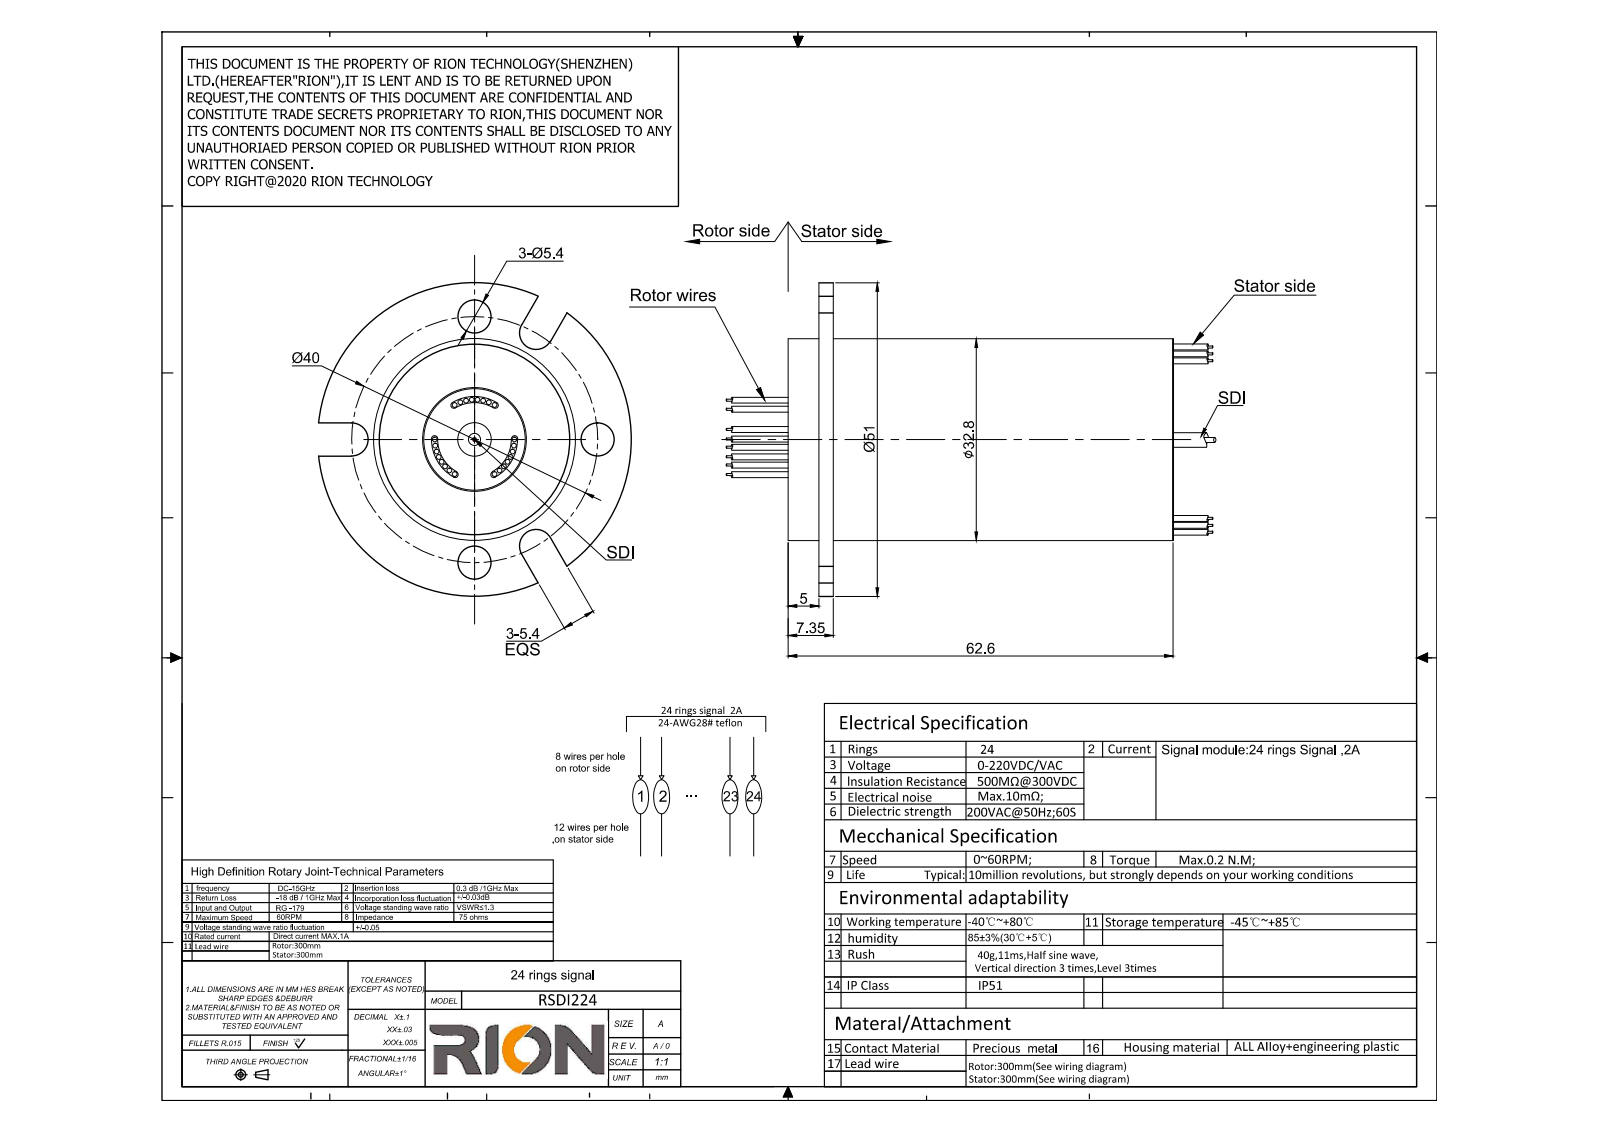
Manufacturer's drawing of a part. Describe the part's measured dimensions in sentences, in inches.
The part is named "MSDI224". Its 3-D file was written by "SolidWorks 2014 (CONFIG_CONTROL_DESIGN)". It is 47 solids with 252 faces: 115 planar, 137 cylindrical and 0 other. Overall it measures 3.252 by 2.008 by 2.002 inches. Its volume is 3.392 cubic inches and its surface area 18.52 square inches. Round holes: 3 of diameter 0.213. Round bosses or shafts: 48 of diameter 0.031, 1 of diameter 2.008, 1 of diameter 1.291, 1 of diameter 0.102. Partial cylindrical surfaces (rounded edges, fillets, slot ends): 6 of radius 0.026, 3 of radius 0.106, 1 of radius 0.217, 1 of radius 0.269, 1 of radius 0.625. The main face-to-face distances are 0.093, 0.197, 0.289, 2.465, 2.268, 2.175, 2.457, 2.26, 2.167, 0.213. The hole center spacings are 1.113, 1.575.
